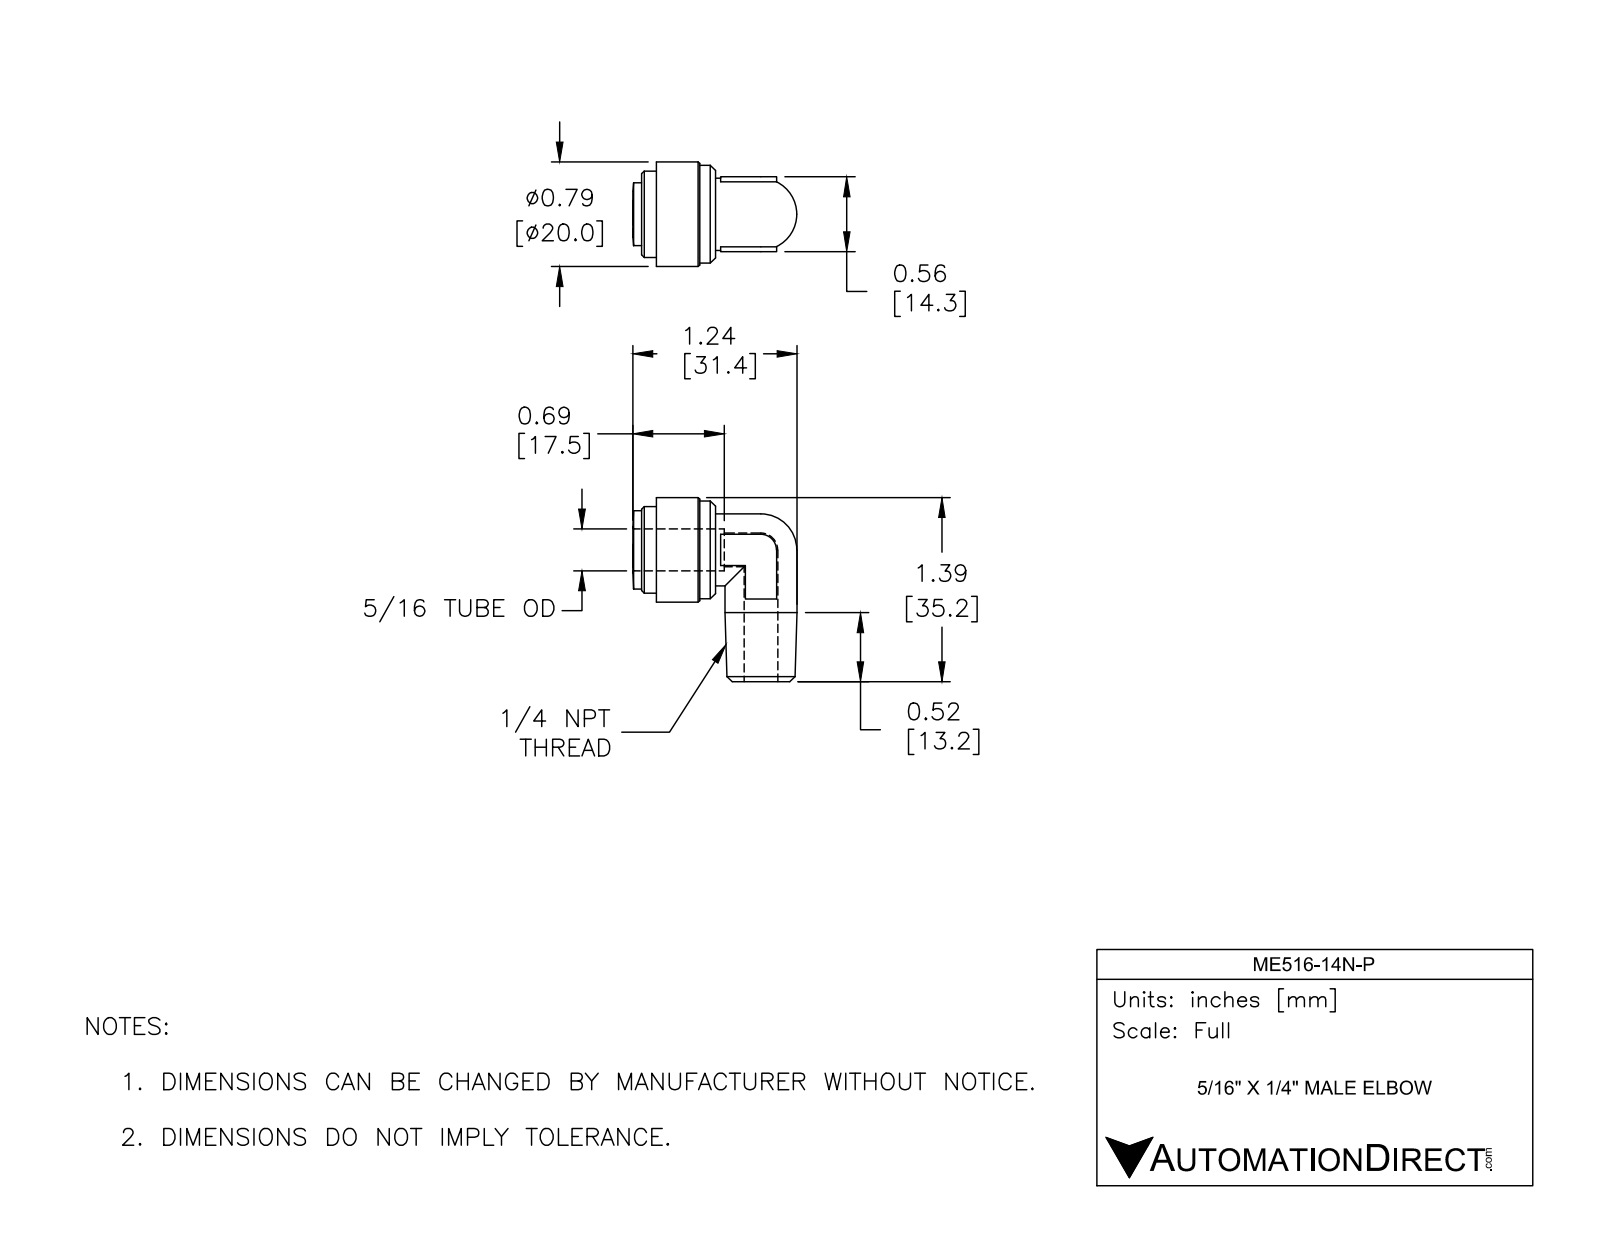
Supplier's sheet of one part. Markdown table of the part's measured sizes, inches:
| quantity | value |
| --- | --- |
| part name | ME516-14N-P |
| STEP written by | SolidWorks 2017 (AUTOMOTIVE_DESIGN) |
| units | inches |
| bodies | 1 solid, 58 faces (20 planar, 18 cylindrical, 20 other) |
| overall size | 1.386 × 1.236 × 0.787 |
| volume | 0.443 in³ |
| surface area | 6.077 in² |
| round holes (diameter × count) | 0.252 × 2, 0.315 × 1 |
| round bosses / shafts (diameter × count) | 0.543 × 2, 0.787 × 1, 0.736 × 1, 0.65 × 1 |
| partial cylindrical surfaces (radius × count) | 0.118 × 1 |
| main face-to-face distances | 0.563, 0.445, 0.11, 0.555, 0.622, 0.185, 0.437, 0.327, 0.118, 0.236 |
